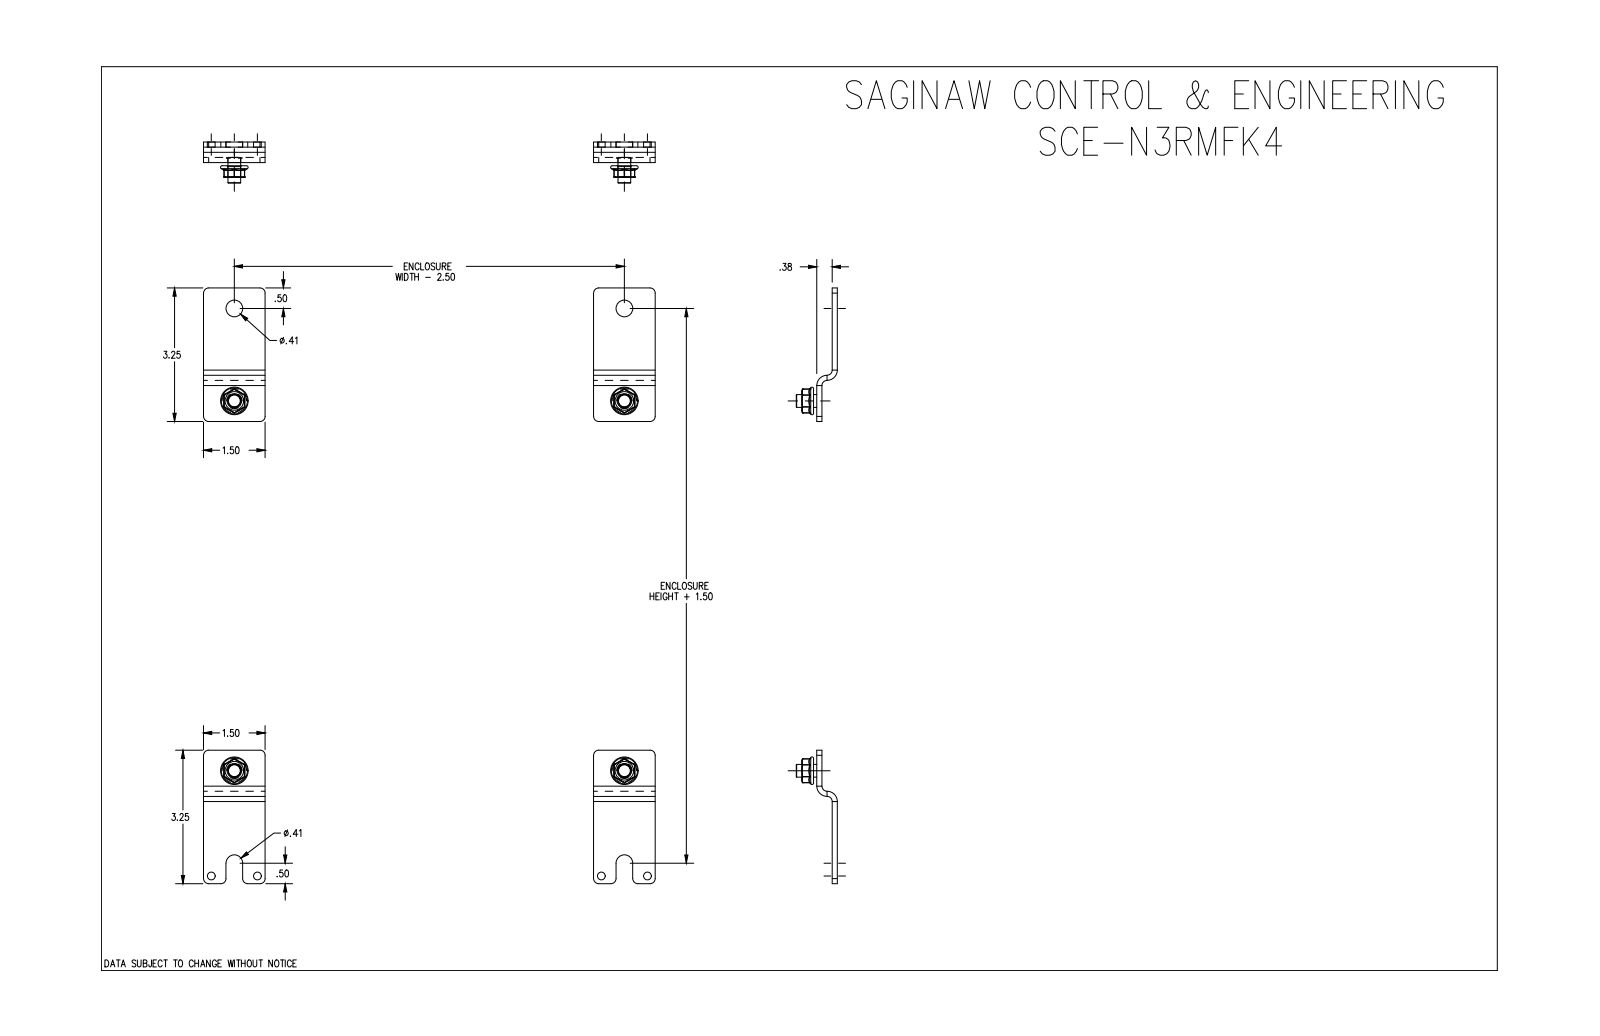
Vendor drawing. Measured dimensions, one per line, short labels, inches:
name: SCE-N3RMFK4
written by: SolidWorks 2019 (CONFIG_CONTROL_DESIGN)
unit: in
bodies: 12 solids, 286 faces (82 planar, 84 cylindrical, 120 other)
size: 14.501 × 11 × 1
volume: 2.832 in³; area: 53.45 in²
holes: 4× ⌀0.188, 4× ⌀0.312, 4× ⌀0.313, 2× ⌀0.406
bosses: 4× ⌀0.376, 4× ⌀0.31
rounds: 24× R0.01, 24× R0.125, 4× R0.25, 2× R0.203
face distances: 0.125, 0.375, 0.25, 0.5, 0.375, 0.125, 9.5, 1.5, 8, 11
hole spacings: 9.5, 2.623, 11.576, 13.824, 1.124, 2.251, 9, 9.298
